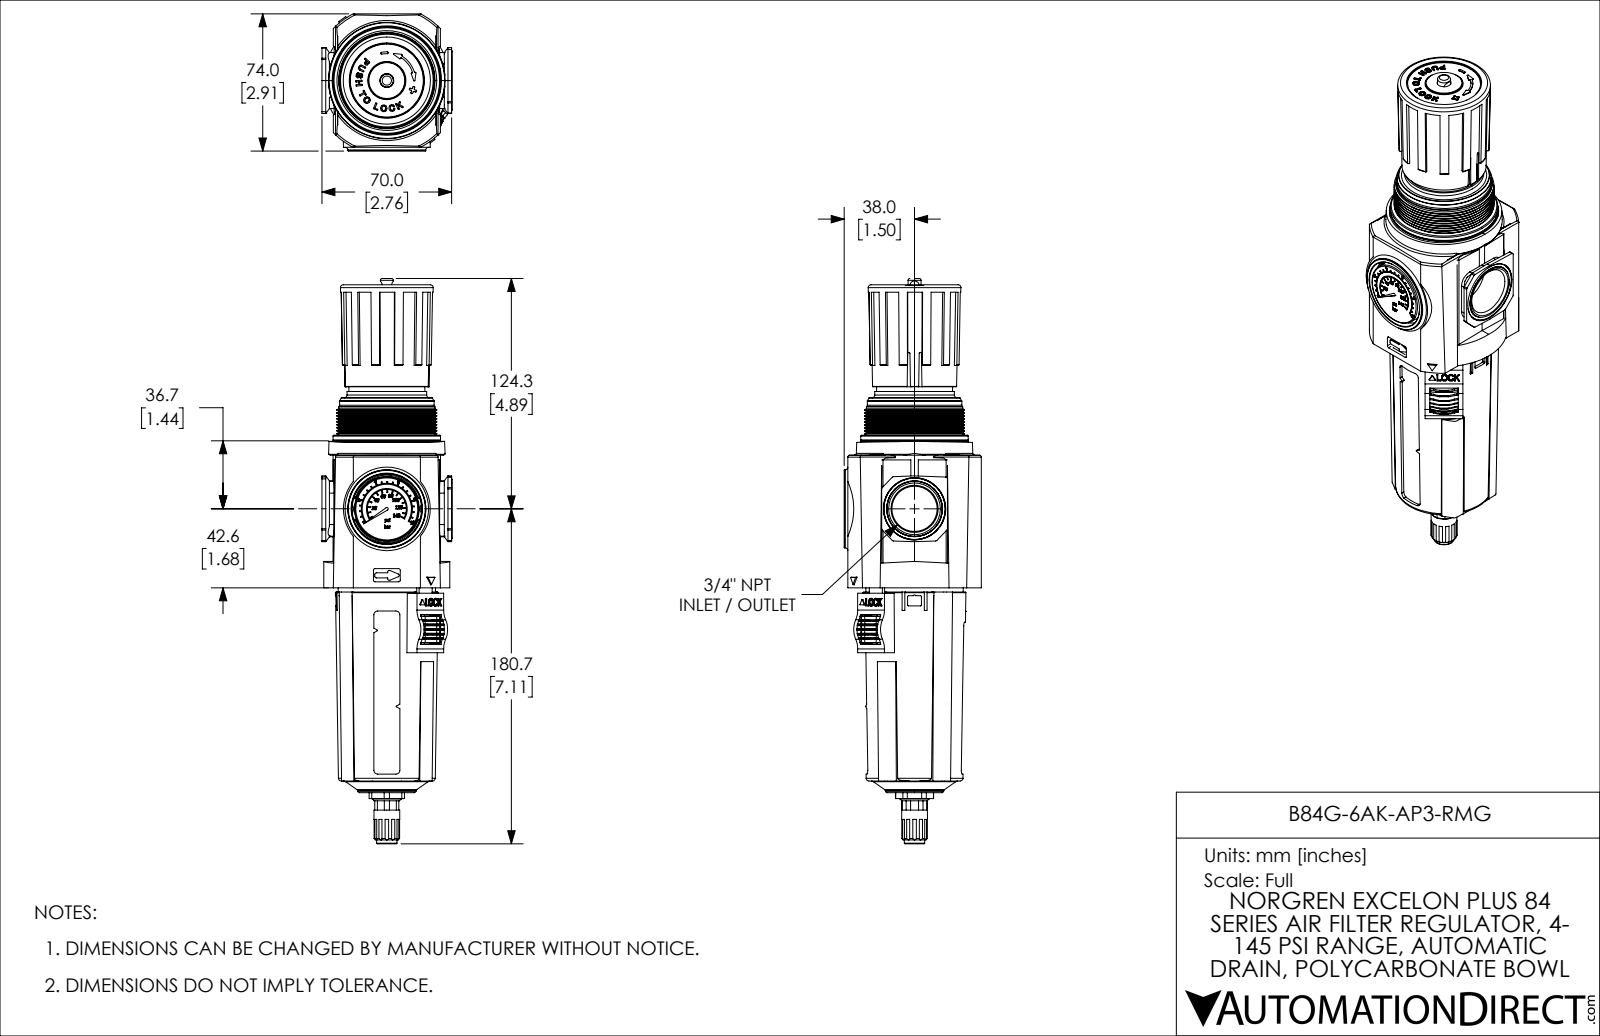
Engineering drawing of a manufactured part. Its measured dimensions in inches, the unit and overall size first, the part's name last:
Units: inches
Overall size (bounding box): 12.005 × 2.913 × 2.766
Round holes (diameter × count): ⌀0.177 ×2, ⌀0.059 ×1, ⌀0.197 ×1, ⌀0.22 ×1, ⌀0.246 ×1, ⌀0.776 ×1, ⌀0.969 ×1, ⌀1.319 ×1, ⌀2.323 ×1, ⌀2.461 ×1
Round bosses / shafts (diameter × count): ⌀0.299 ×2, ⌀0.157 ×2, ⌀2.283 ×1, ⌀2.119 ×1, ⌀2.047 ×1, ⌀2.026 ×1, ⌀2.008 ×1, ⌀1.693 ×1
Partial cylindrical surfaces — rounded edges, fillets, slot ends (radius × count): R0.039 ×34, R0.012 ×27, R0.02 ×26, R0.01 ×24, R0.047 ×18, R0.028 ×16, R0.03 ×16, R0.004 ×14
Main face-to-face distances: 2.719, 2.323, 0.035, 2.683, 0.512, 0.622, 2.096, 2.061, 3.866, 3.831
Hole centre spacings: 0.856, 1.713
Volume: 45.52 in³ · Surface area: 208.4 in²
Bodies: 8 solids, 2561 faces (955 planar, 1193 cylindrical, 413 other)
Part name (STEP PRODUCT): B84G-6AK-AP3-RMG
STEP written by: SolidWorks 2021 (CONFIG_CONTROL_DESIGN)
